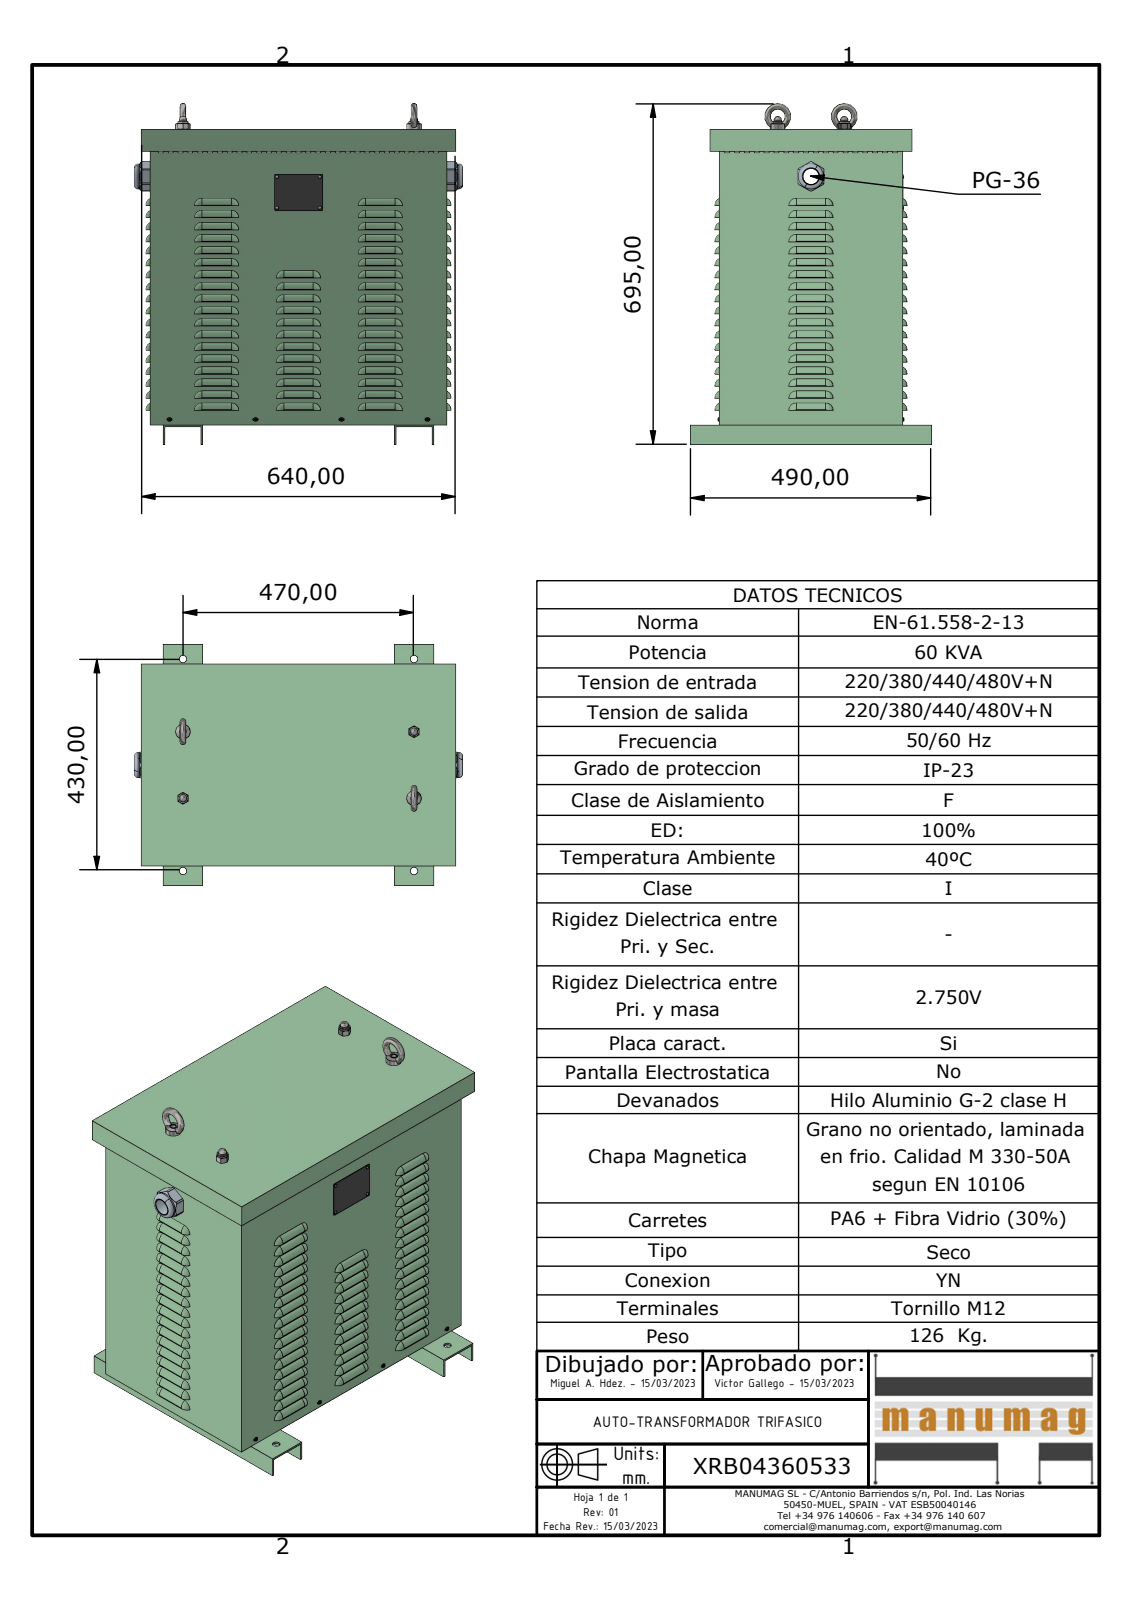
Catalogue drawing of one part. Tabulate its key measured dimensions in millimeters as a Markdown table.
| quantity | value |
| --- | --- |
| part name | XRB04360533; JE060 - JE075 CUERPO; JE060 - JE075 BASE; JE060 TAPA SUPERIOR (+7 more) |
| STEP written by | Autodesk Inventor 2023 (AUTOMOTIVE_DESIGN) |
| units | millimeters |
| bodies | 24 solids, 2907 faces (1145 planar, 1024 cylindrical, 738 other) |
| overall size | 695 × 668.2 × 490 |
| volume | 4 615 000 mm³ |
| surface area | 4 047 000 mm² |
| round holes (diameter × count) | 11 × 364, 15 × 8, 4 × 4, 5 × 4, 10.11 × 2, 11.84 × 2, 32 × 1, 48 × 1 |
| round bosses / shafts (diameter × count) | 4 × 4, 3.62 × 4, 3.2 × 4, 51.1 × 2, 30 × 2, 21 × 2, 15.6 × 2, 47.45 × 1 |
| partial cylindrical surfaces (radius × count) | 14 × 132, 7 × 72, 15 × 72, 3.88 × 12, 2.5 × 8, 7.5 × 8, 2 × 4, 30 × 2 |
| main face-to-face distances | 2, 370, 600, 601, 368, 372, 602, 599, 598, 603 |
| hole center spacings | 30, 21.21, 132, 128.88, 147, 173.76, 279, 469.24 |
